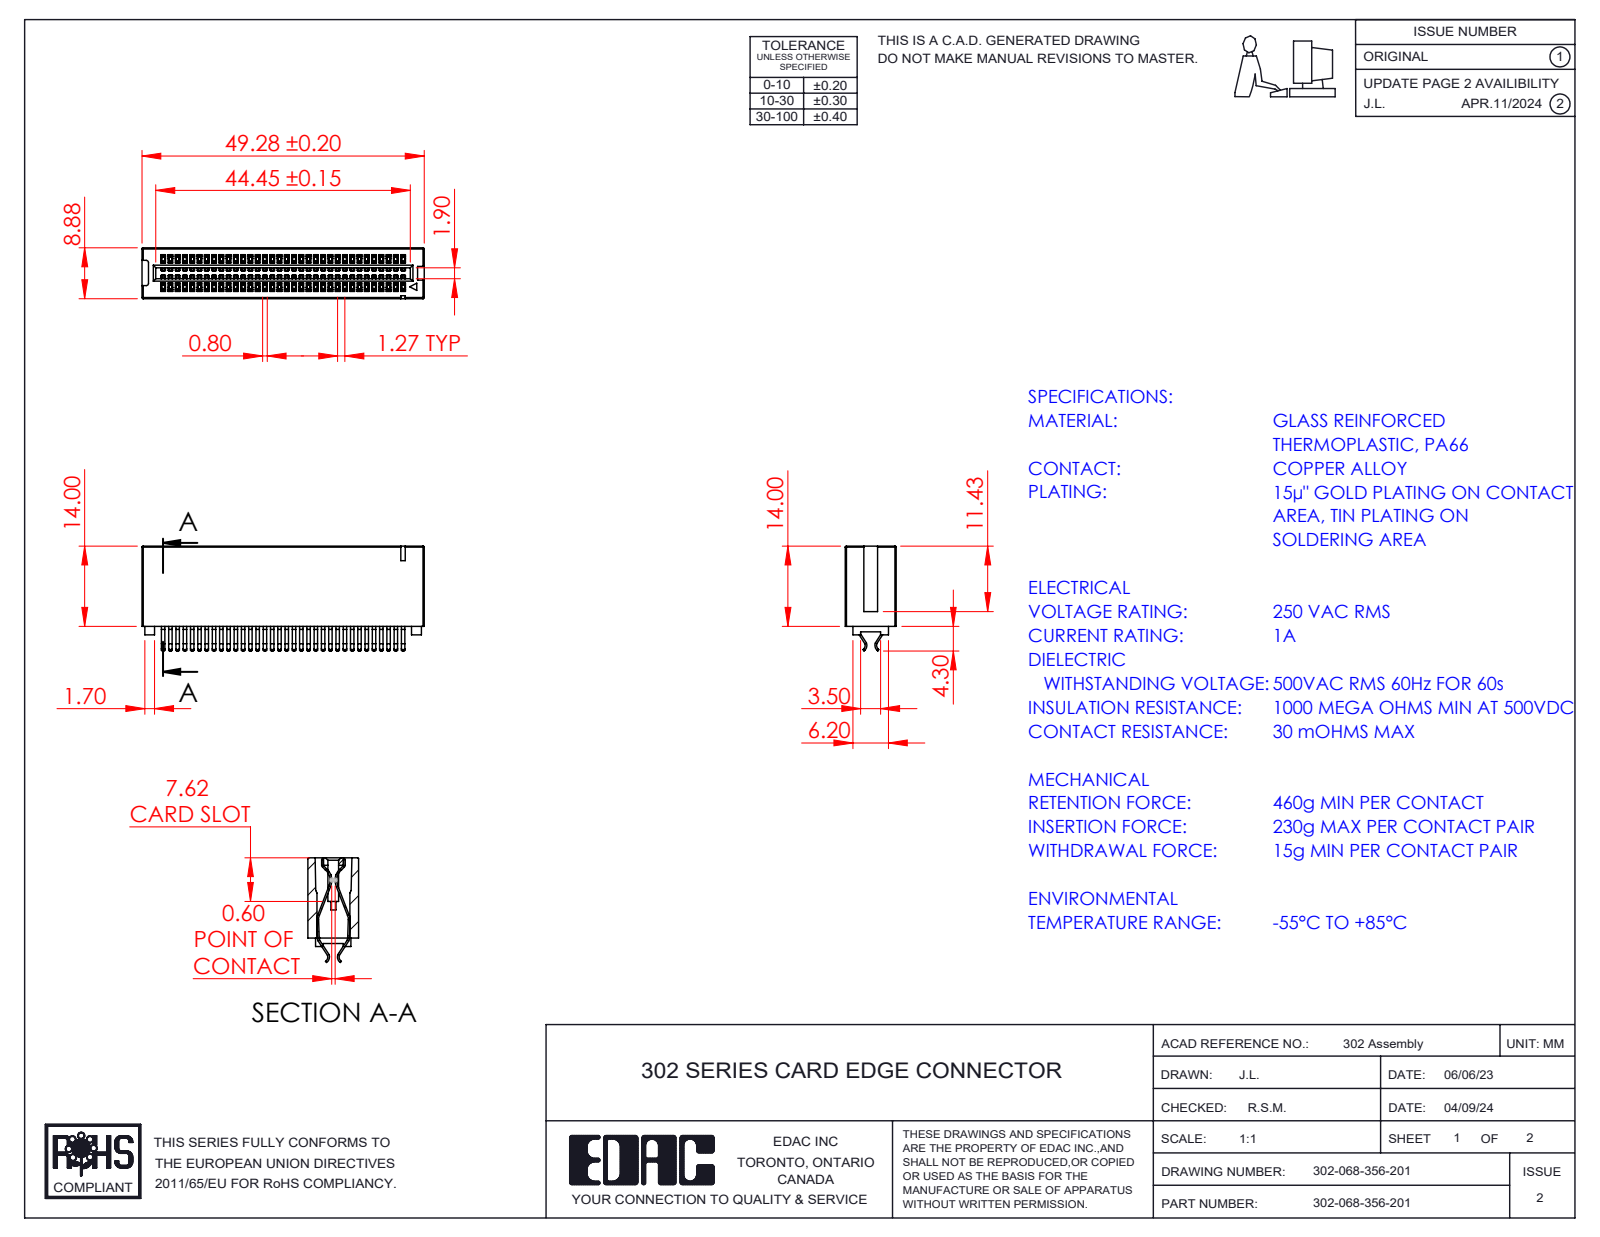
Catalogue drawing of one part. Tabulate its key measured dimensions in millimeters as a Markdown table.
| quantity | value |
| --- | --- |
| part name | Contact_302-290-X56; 302-068-356-201; HSG_Vertical HSG |
| STEP written by | SolidWorks 2023 (CONFIG_CONTROL_DESIGN) |
| units | millimeters |
| bodies | 69 solids, 3296 faces (2191 planar, 1101 cylindrical, 4 other) |
| overall size | 49.28 × 18.3 × 8.88 |
| volume | 3 848 mm³ |
| surface area | 10 564 mm² |
| partial cylindrical surfaces (radius × count) | 0.2 × 212, 0.11 × 2, 0.4 × 2, 0.41 × 2, 0.93 × 2, 1.05 × 2, 1.23 × 2, 1.25 × 2 |
| main face-to-face distances | 1.27, 2.54, 8.88, 3.81, 0.8, 5.08, 0.47, 2.07, 3.34, 6.35 |
